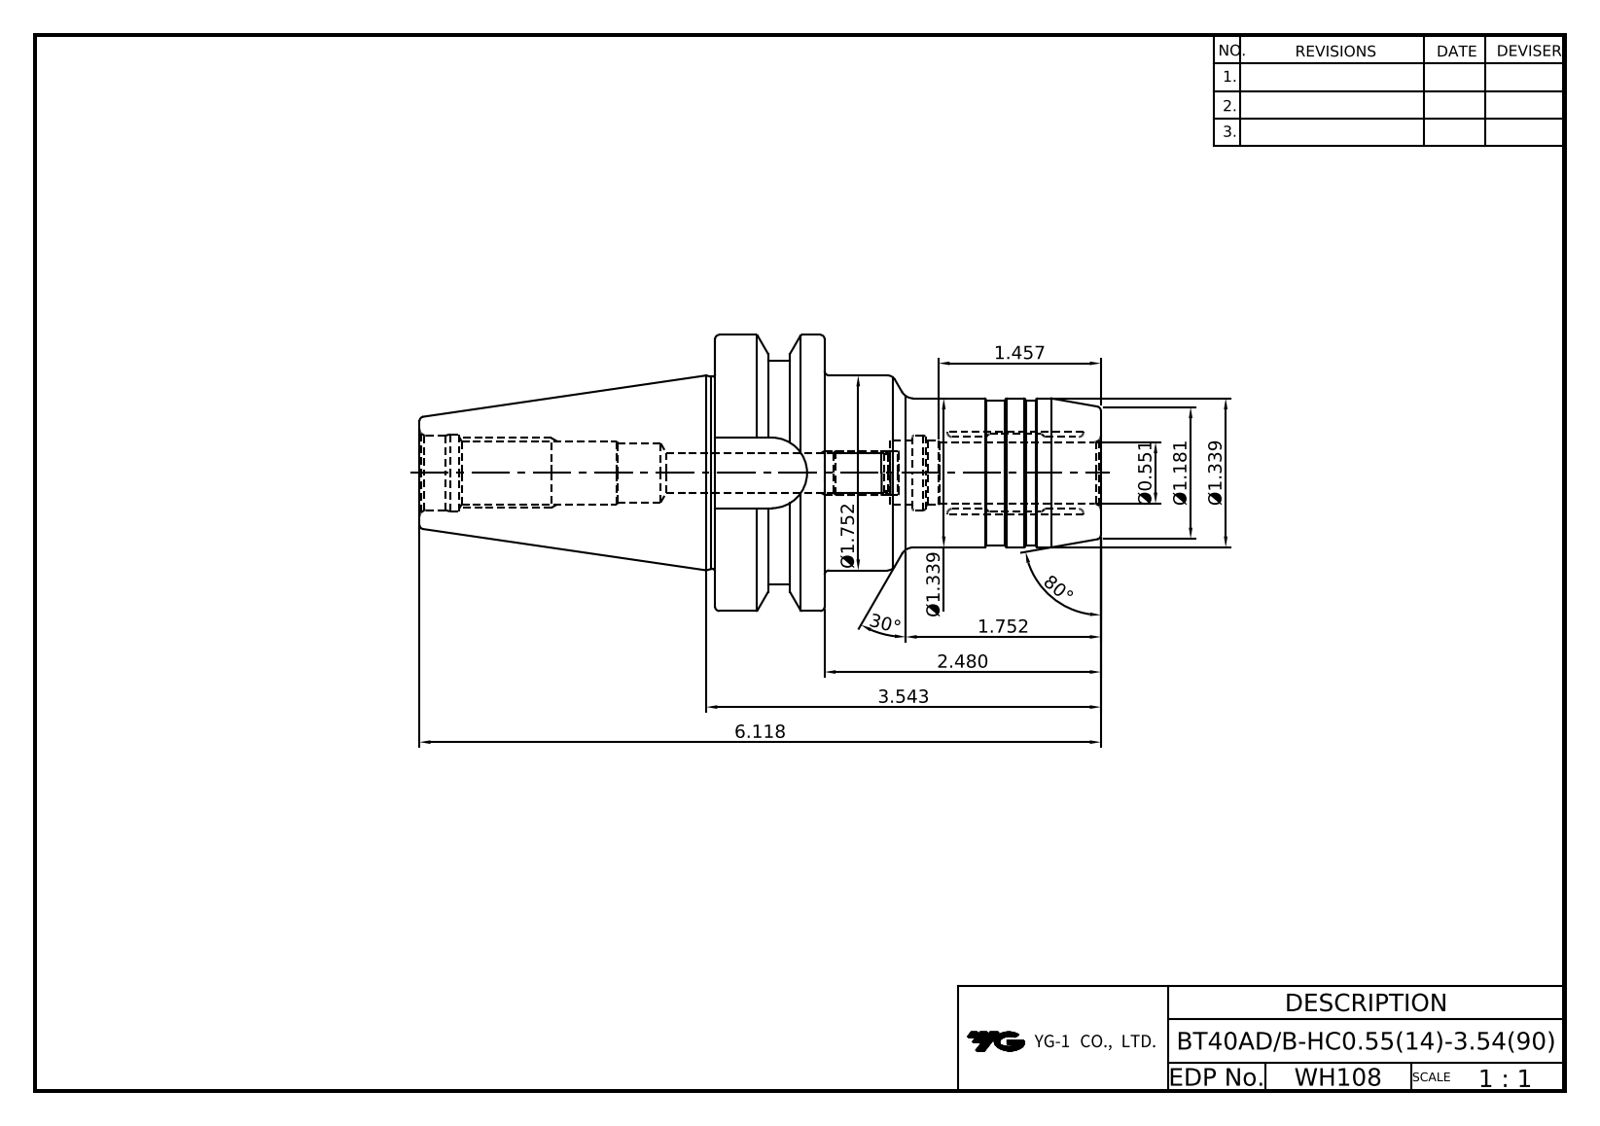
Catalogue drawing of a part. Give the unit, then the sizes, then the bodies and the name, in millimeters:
Units: millimetres
Overall size (bounding box): 155.4 × 63 × 63
Round holes (diameter × count): ⌀3.24 ×4, ⌀4 ×4, ⌀8.92 ×1, ⌀13.5 ×1, ⌀13.84 ×1, ⌀14 ×1, ⌀14.6 ×1, ⌀17 ×1, ⌀17.6 ×1
Round bosses / shafts (diameter × count): ⌀63 ×1, ⌀51 ×1, ⌀44.5 ×1, ⌀44 ×1, ⌀34 ×1, ⌀33 ×1
Partial cylindrical surfaces — rounded edges, fillets, slot ends (radius × count): R8.05 ×1
Main face-to-face distances: 25, 88, 63, 45.2, 5, 17.1, 7.9, 70.9, 12.1, 12.9
Volume: 179 786 mm³ · Surface area: 32 231 mm²
Bodies: 1 solid, 88 faces (21 planar, 33 cylindrical, 34 other)
Part name (STEP PRODUCT): LO-BT40ADB-HC14-90
STEP written by: Autodesk Inventor 2022 (AUTOMOTIVE_DESIGN)
